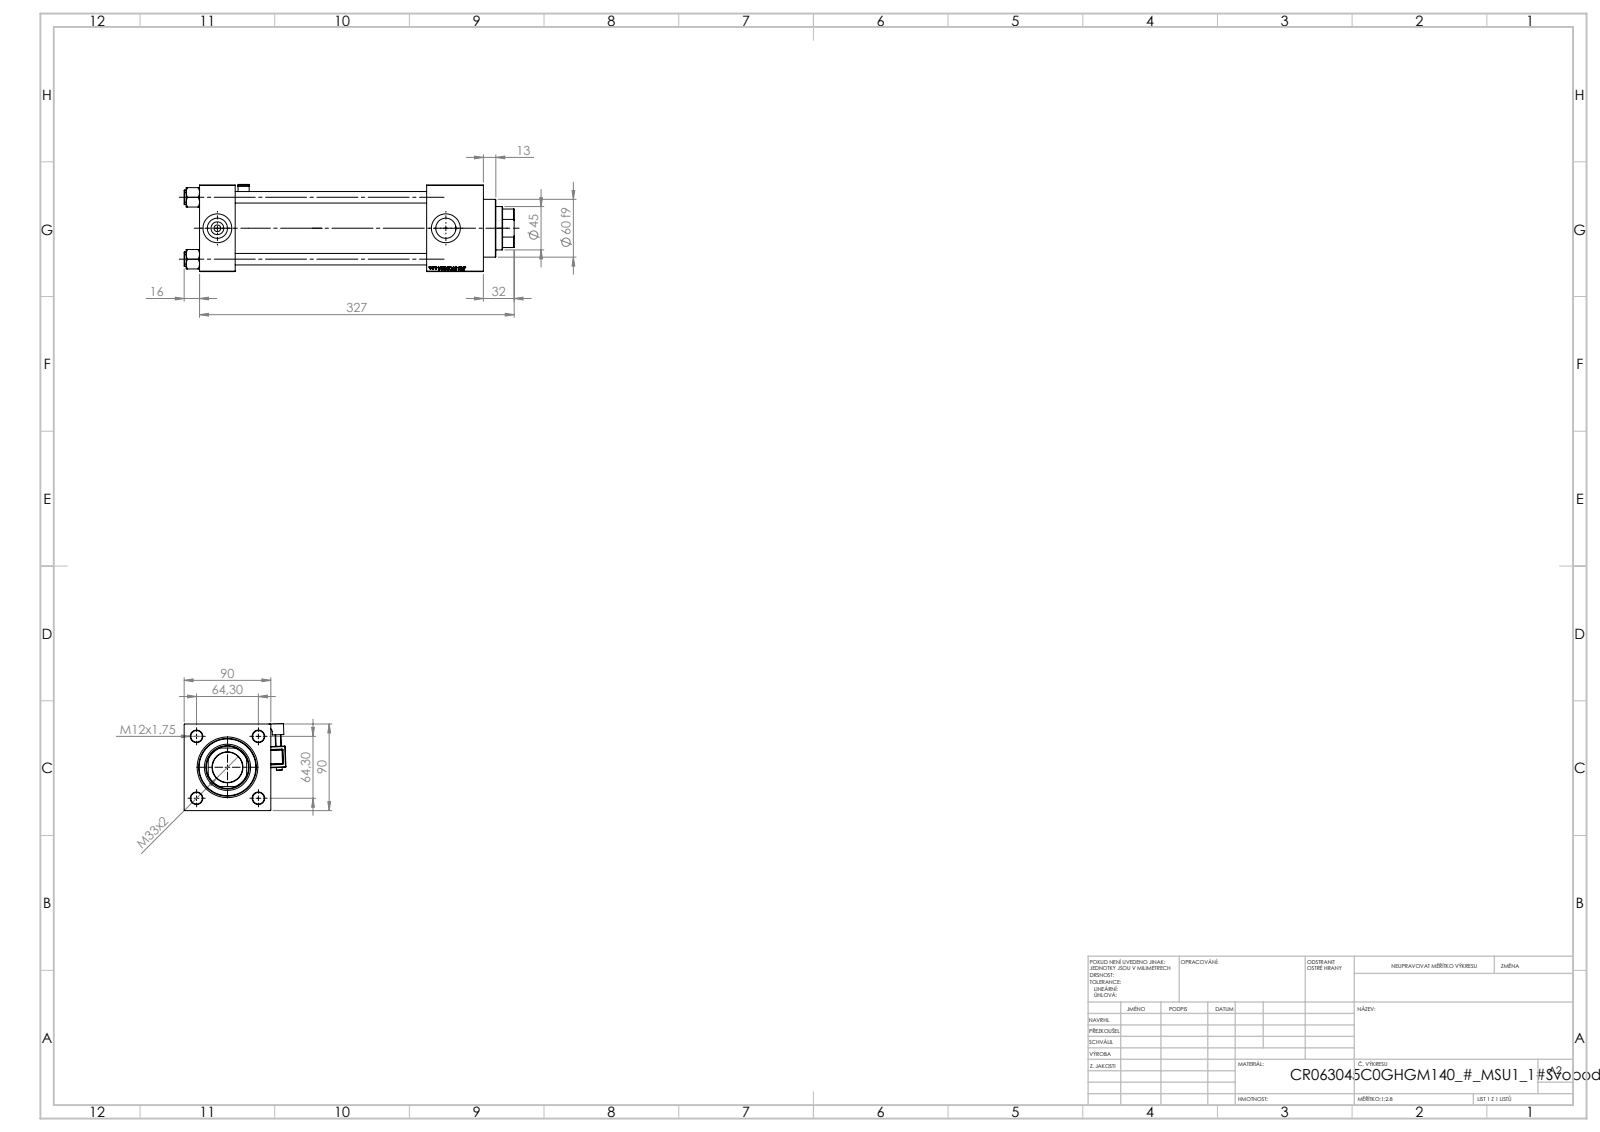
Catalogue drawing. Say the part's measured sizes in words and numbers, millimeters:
The part is named "V215CR_MSU; NUT_M5_C; V215CR_C_TYCINKA; V215_VC_A (+2 more)". Its 3-D file was written by "SolidWorks 2019 (CONFIG_CONTROL_DESIGN)". It is 12 solids with 1222 faces: 554 planar, 114 cylindrical and 554 other. Overall it measures 343 by 105.78 by 90.53 millimeters. Its volume is 1 392 000 cubic millimeters and its surface area 295 025 square millimeters. Round holes: 4 of diameter 12, 2 of diameter 7, 2 of diameter 20.96, 2 of diameter 30, 1 of diameter 31.5, 1 of diameter 45, 1 of diameter 48, 1 of diameter 50, 1 of diameter 60, 1 of diameter 63. Round bosses or shafts: 4 of diameter 15, 1 of diameter 69, 1 of diameter 6. Partial cylindrical surfaces (rounded edges, fillets, slot ends): 24 of radius 0.5, 1 of radius 1, 1 of radius 2.5, 1 of radius 4, 1 of radius 22. The main face-to-face distances are 90, 37, 59, 236, 199, 295, 258, 266.3, 229.3, 30.3. The hole center spacings are 45.47, 64.3, 90.93, 237.5.
